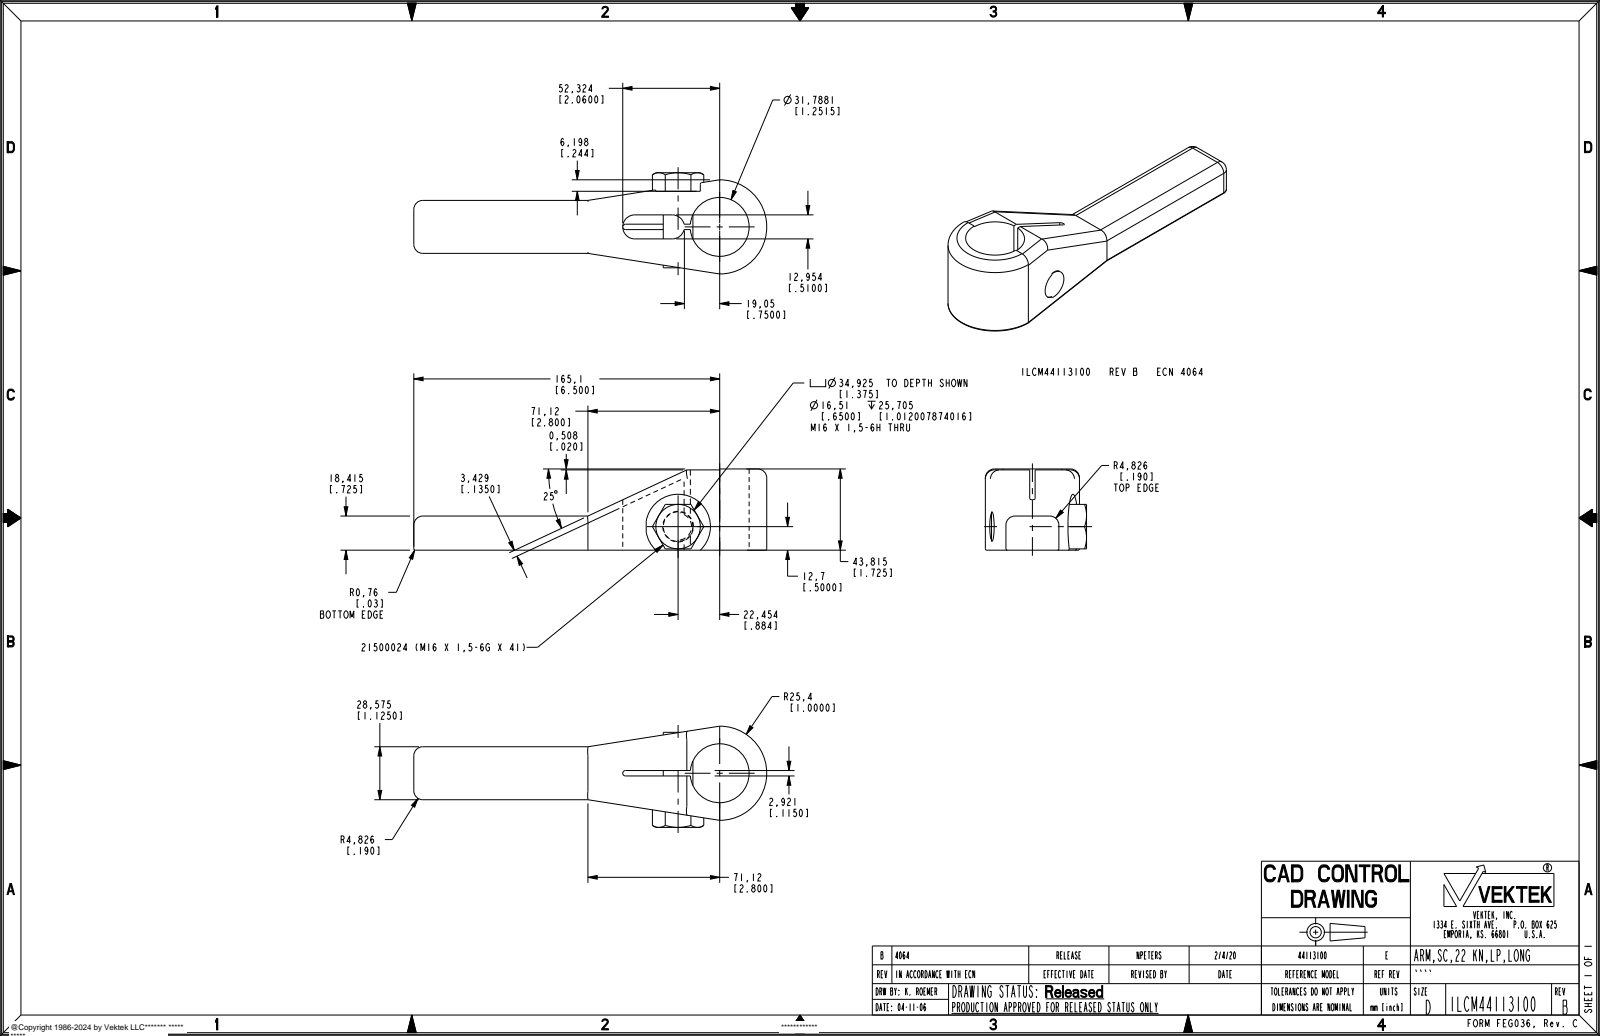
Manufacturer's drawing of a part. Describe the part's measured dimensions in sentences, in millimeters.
The part is named "ILCM44113100". Its 3-D file was written by "PRO/ENGINEER BY PARAMETRIC TECHNOLOGY CORPORATION, 2013320 (AUTOMOTIVE_DESIGN)". It is 1 solid with 76 faces: 32 planar, 32 cylindrical and 12 other. Overall it measures 190.5 by 54.61 by 43.81 millimeters. Its volume is 147 771 cubic millimeters and its surface area 32 454 square millimeters. Round holes: 1 of diameter 16.51, 1 of diameter 31.79. Round bosses or shafts: 1 of diameter 16. Partial cylindrical surfaces (rounded edges, fillets, slot ends): 9 of radius 4.83, 5 of radius 0.76, 2 of radius 6.48, 1 of radius 1.46, 1 of radius 7.26, 1 of radius 17.46, 1 of radius 25.4. The main face-to-face distances are 18.41, 7.81, 20.77, 28.58, 12.96, 14.92, 22.73, 35.69, 43.5, 12.83.
